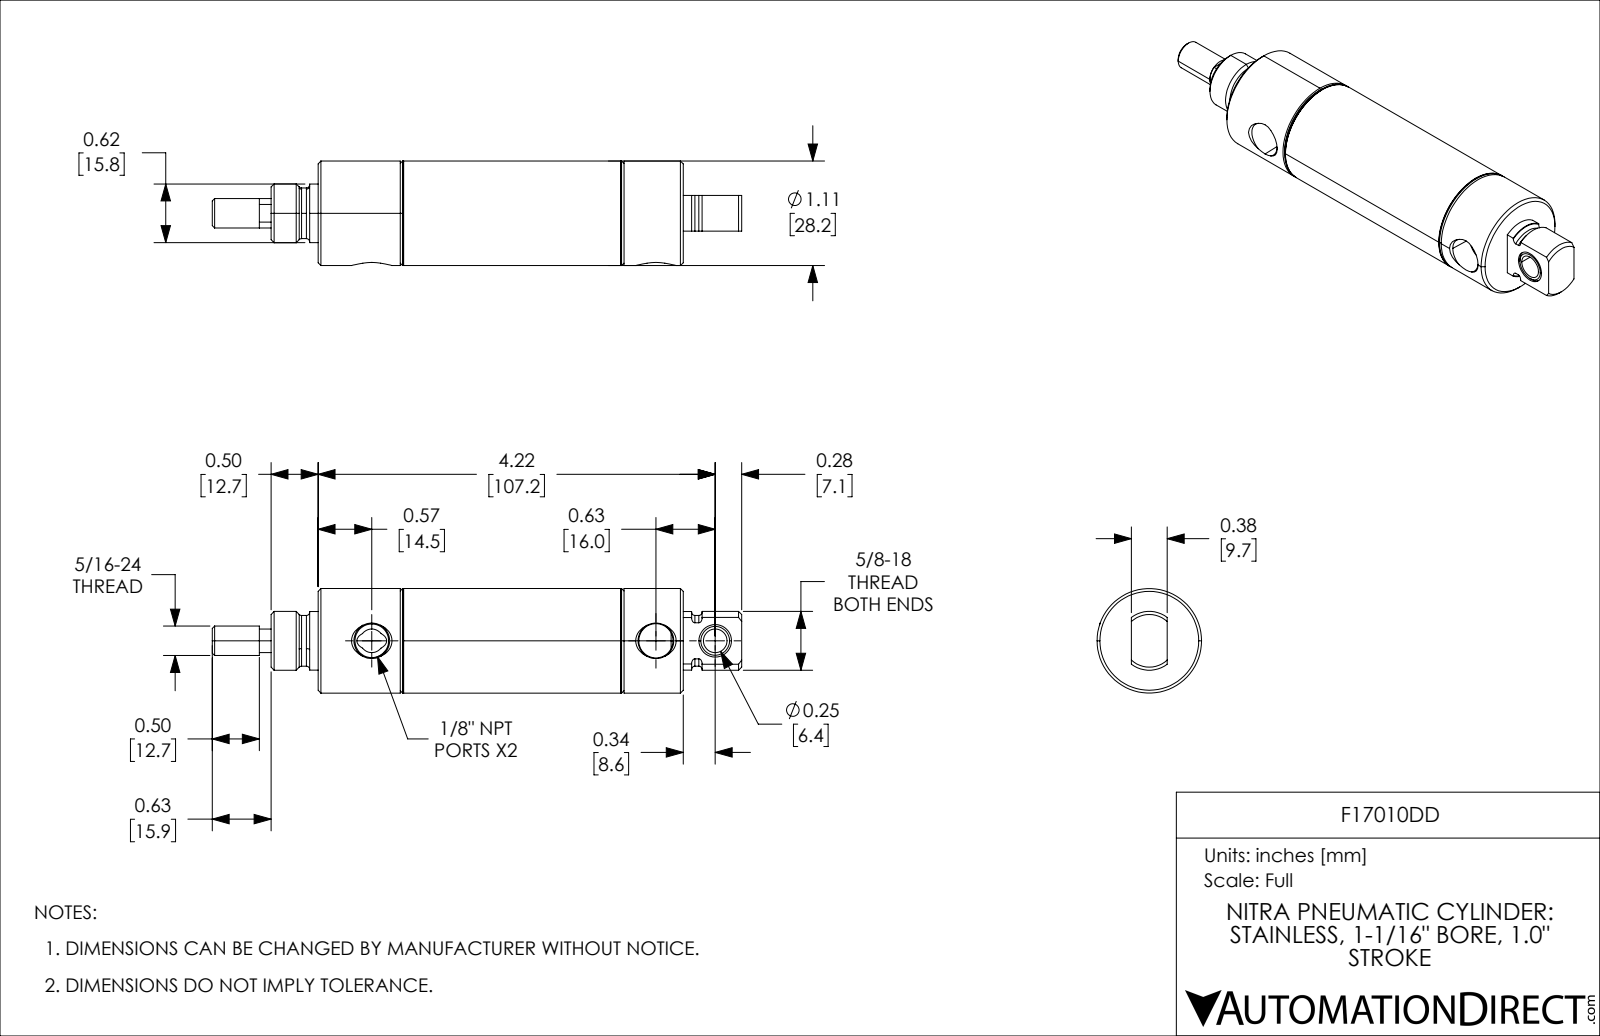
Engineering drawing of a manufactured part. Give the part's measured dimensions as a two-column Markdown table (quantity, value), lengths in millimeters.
| quantity | value |
| --- | --- |
| part name | F17010DD_11; F17010DD_9; F17010DD; F17010DD_5 (+2 more) |
| STEP written by | SolidWorks 2021 (CONFIG_CONTROL_DESIGN) |
| units | millimeters |
| bodies | 5 solids, 156 faces (30 planar, 58 cylindrical, 68 other) |
| overall size | 142.88 × 28.19 × 28.19 |
| volume | 48 173 mm³ |
| surface area | 27 195 mm² |
| round holes (diameter × count) | 6.38 × 1, 8.53 × 1, 8.78 × 1, 9.25 × 1, 9.53 × 1, 19.05 × 1, 25.7 × 1 |
| round bosses / shafts (diameter × count) | 28.19 × 1, 27.23 × 1, 15.88 × 1, 15.81 × 1, 13.68 × 1, 7.94 × 1, 7.92 × 1 |
| partial cylindrical surfaces (radius × count) | 3.17 × 1, 6.84 × 1 |
| main face-to-face distances | 22.22, 25.4, 47.62, 69.95, 44.55, 22.33, 28.58, 53.98, 76.2, 98.53 |
| hole center spacings | 16.01 |
